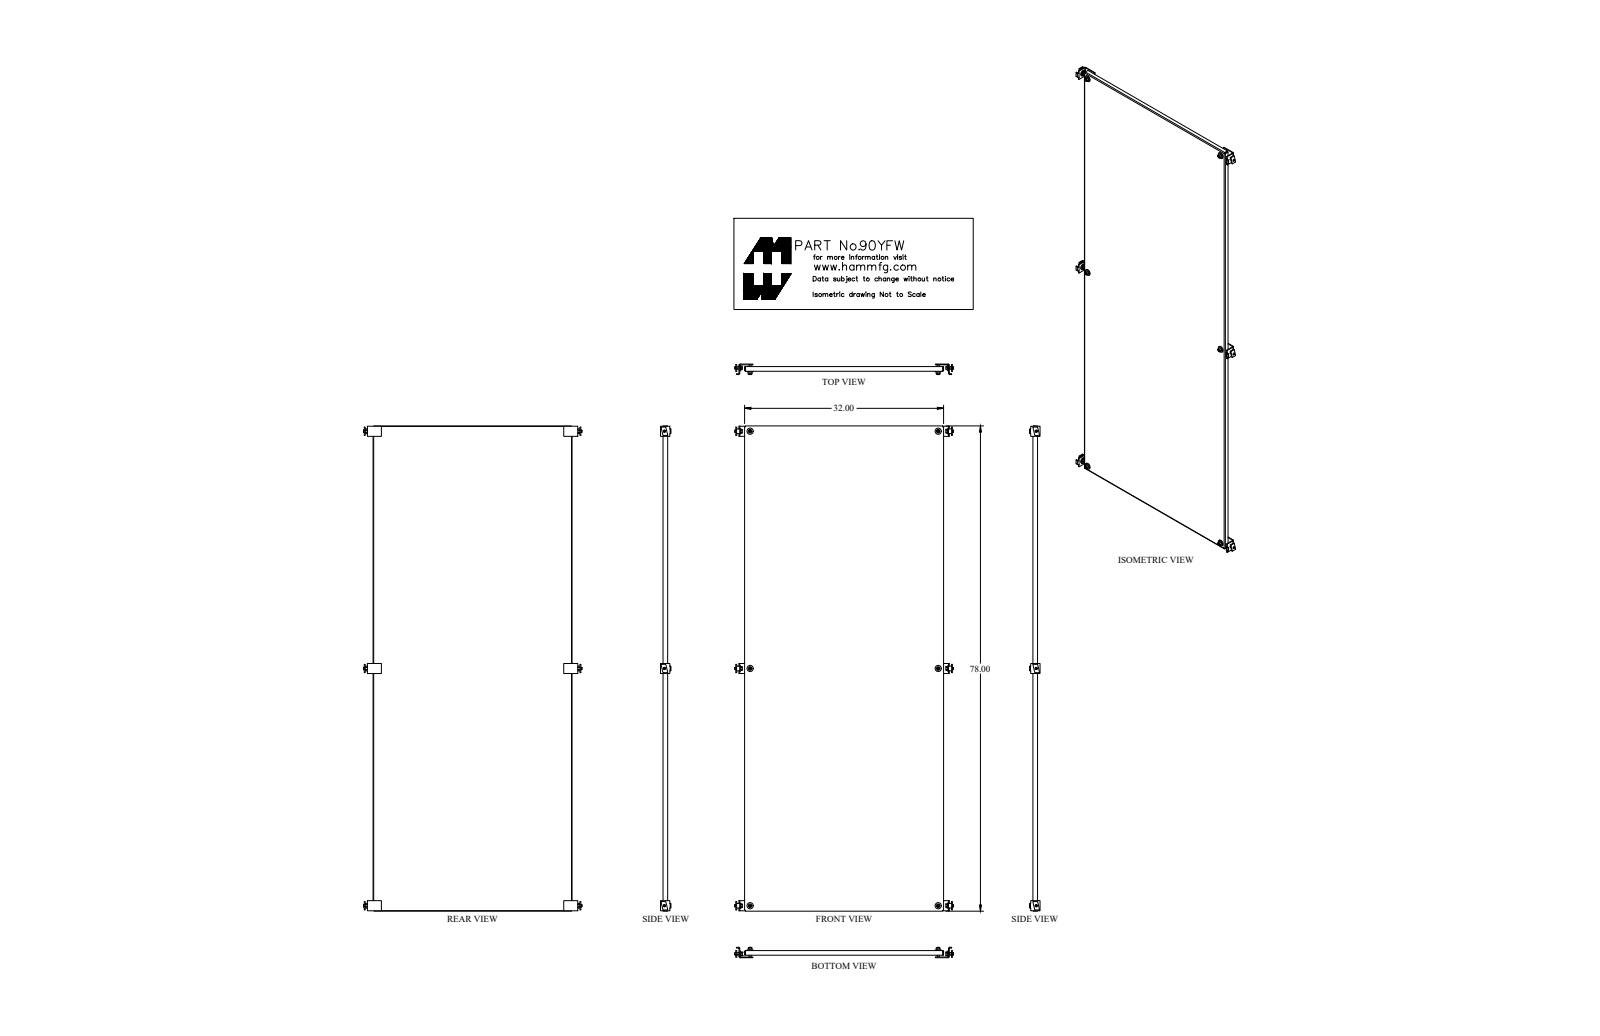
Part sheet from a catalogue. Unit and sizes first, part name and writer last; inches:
Units: inches
Overall size (bounding box): 78 × 32 × 0.75
Round holes (diameter × count): ⌀0.563 ×6
Partial cylindrical surfaces — rounded edges, fillets, slot ends (radius × count): R0.048 ×4, R0.143 ×4
Main face-to-face distances: 0.095, 31.905, 31.81, 32, 77.905, 0.75, 0.655, 78, 77.81, 0.143
Hole centre spacings: 38.125, 48.669, 30.25, 76.25, 82.032
Volume: 249.7 in³ · Surface area: 5 280 in²
Bodies: 1 solid, 42 faces (22 planar, 20 cylindrical, 0 other)
Part name (STEP PRODUCT): 90YFW_Default
STEP written by: SolidWorks 2018 (CONFIG_CONTROL_DESIGN)
